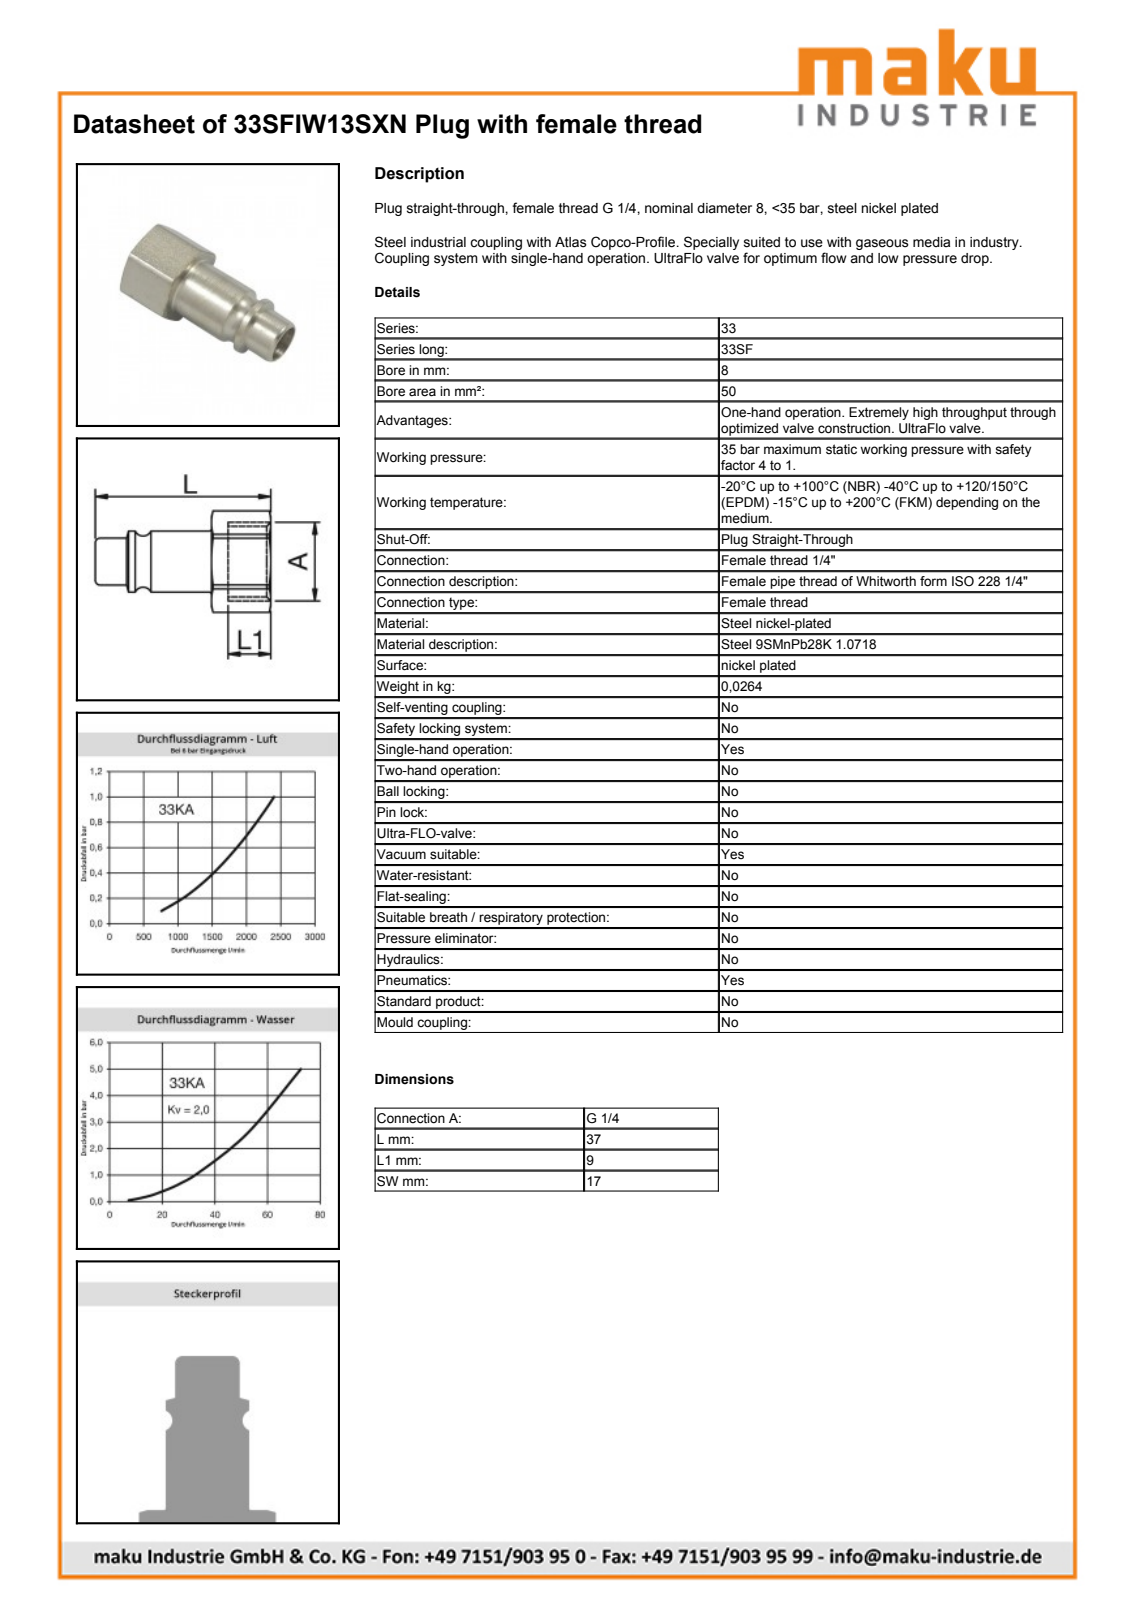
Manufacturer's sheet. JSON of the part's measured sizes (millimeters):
{"part_name": "D108552", "step_written_by": "Autodesk Inventor 2013 (AUTOMOTIVE_DESIGN)", "units": "millimeters", "bodies": {"solids": 1, "faces": 38, "planar": 10, "cylindrical": 11, "other": 17}, "overall_size": [37, 19.15, 17], "volume_mm3": 3576, "surface_area_mm2": 3020, "round_holes": [[7.8, 1], [11.45, 1]], "round_bosses_or_shafts": [[12.9, 1], [9.9, 1]], "partial_cylinders_radius": [[9.57, 1]], "face_to_face_distances": [17, 12.5, 3.5, 9, 24.5, 28, 37]}
